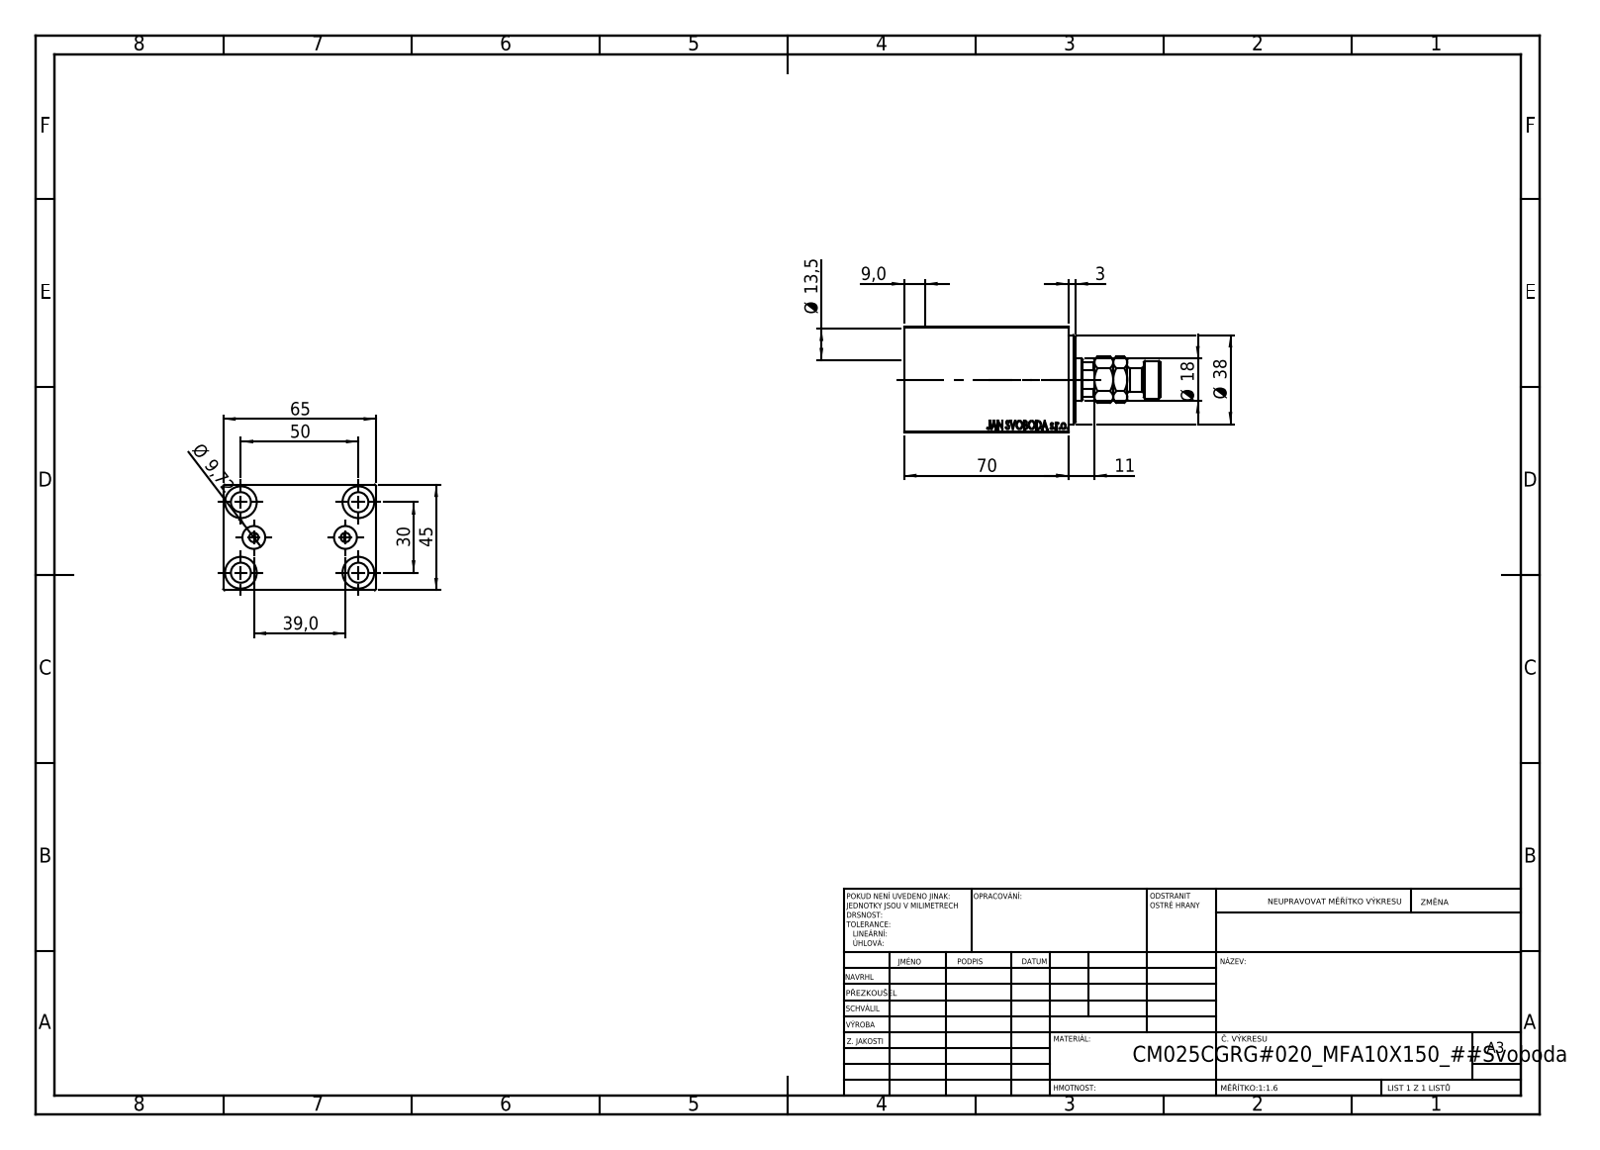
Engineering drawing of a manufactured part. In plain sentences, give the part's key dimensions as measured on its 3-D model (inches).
The part is named "V450CM_C_Body; V450CM_VC_B; V450CM_C_VCP; MFA". Its 3-D file was written by "SolidWorks 2019 (CONFIG_CONTROL_DESIGN)". It is 4 solids with 910 faces: 424 planar, 60 cylindrical and 426 other. Overall it measures 4.291 by 2.559 by 1.772 inches. Its volume is 11.25 cubic inches and its surface area 75.93 square inches. Round holes: 5 of diameter 0.335, 4 of diameter 0.531, 2 of diameter 0.157, 2 of diameter 0.383, 1 of diameter 0.709, 1 of diameter 0.846, 1 of diameter 0.984, 1 of diameter 1.063, 1 of diameter 1.496. Round bosses or shafts: 1 of diameter 0.63, 1 of diameter 0.394. Partial cylindrical surfaces (rounded edges, fillets, slot ends): 1 of radius 0.335. The main face-to-face distances are 1.772, 2.559, 0.236, 2.323, 2.52, 2.756, 0.197, 0.118, 0.315, 0.433. The hole center spacings are 0.629, 1.148, 1.849, 0.768, 1.181, 1.969, 2.296, 1.535.
